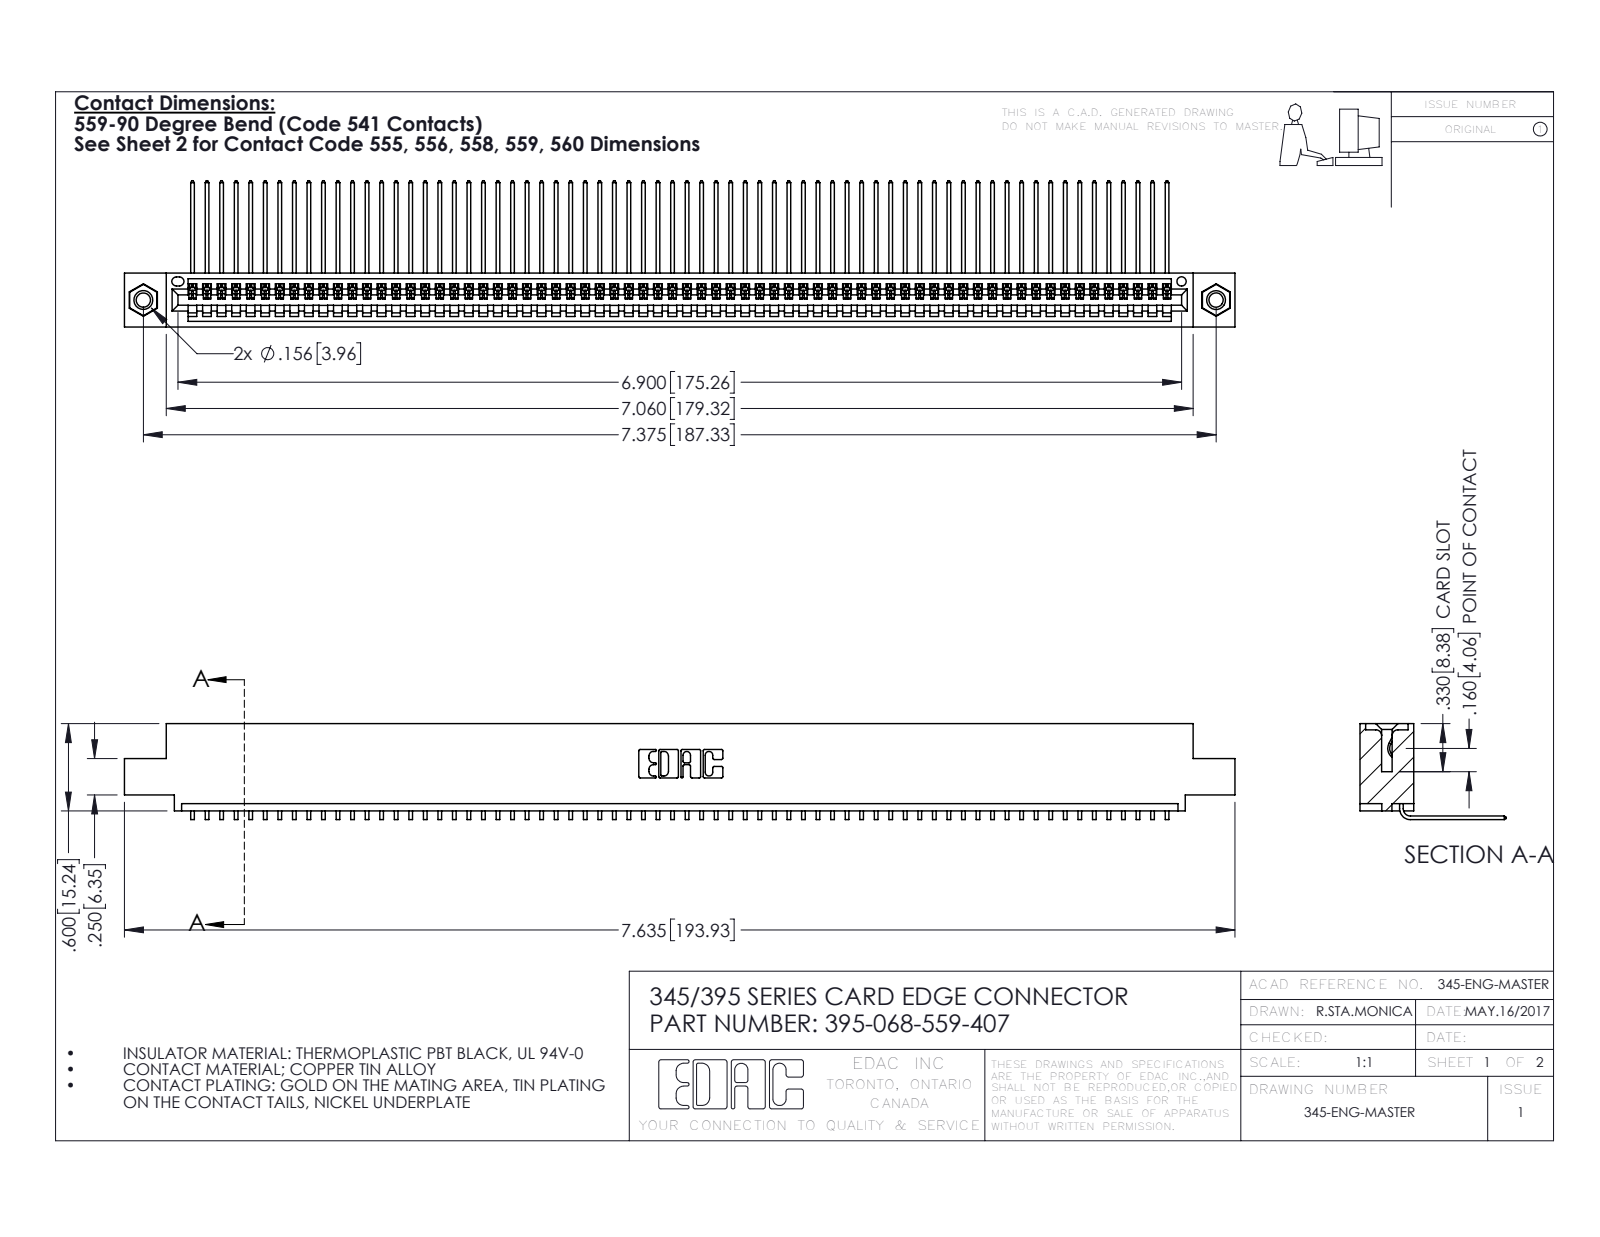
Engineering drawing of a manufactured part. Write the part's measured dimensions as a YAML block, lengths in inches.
part_name: "345-250-001_345-250-005-103; 345-292-001_558 559 Tail - 1; 345 Part_0.110 Offset - 0.156 Dia-TI; 395-068-559-407"
step_written_by: "SolidWorks 2016 (CONFIG_CONTROL_DESIGN)"
units: inches
bodies: {solids: 71, faces: 4270, planar: 2972, cylindrical: 1282, other: 16}
overall_size: [7.635, 1.005, 0.659]
volume: 1.146
surface_area: 41.46
round_holes:
  - {diameter: 0.098, count: 2}
  - {diameter: 0.125, count: 2}
  - {diameter: 0.156, count: 2}
  - {diameter: 0.064, count: 1}
round_bosses_or_shafts:
  - {diameter: 0.155, count: 2}
partial_cylinders:
  - {radius: 0.006, count: 136}
  - {radius: 0.01, count: 22}
  - {radius: 0.007, count: 6}
  - {radius: 0.031, count: 6}
  - {radius: 0.026, count: 3}
  - {radius: 0.031, count: 2}
  - {radius: 0.04, count: 2}
  - {radius: 0.014, count: 1}
face_to_face_distances: [0.072, 0.298, 0.37, 0.2, 0.098, 0.272, 0.025, 0.225, 0.149, 0.072]
hole_center_spacings: [0.27, 7.139, 7.375]
